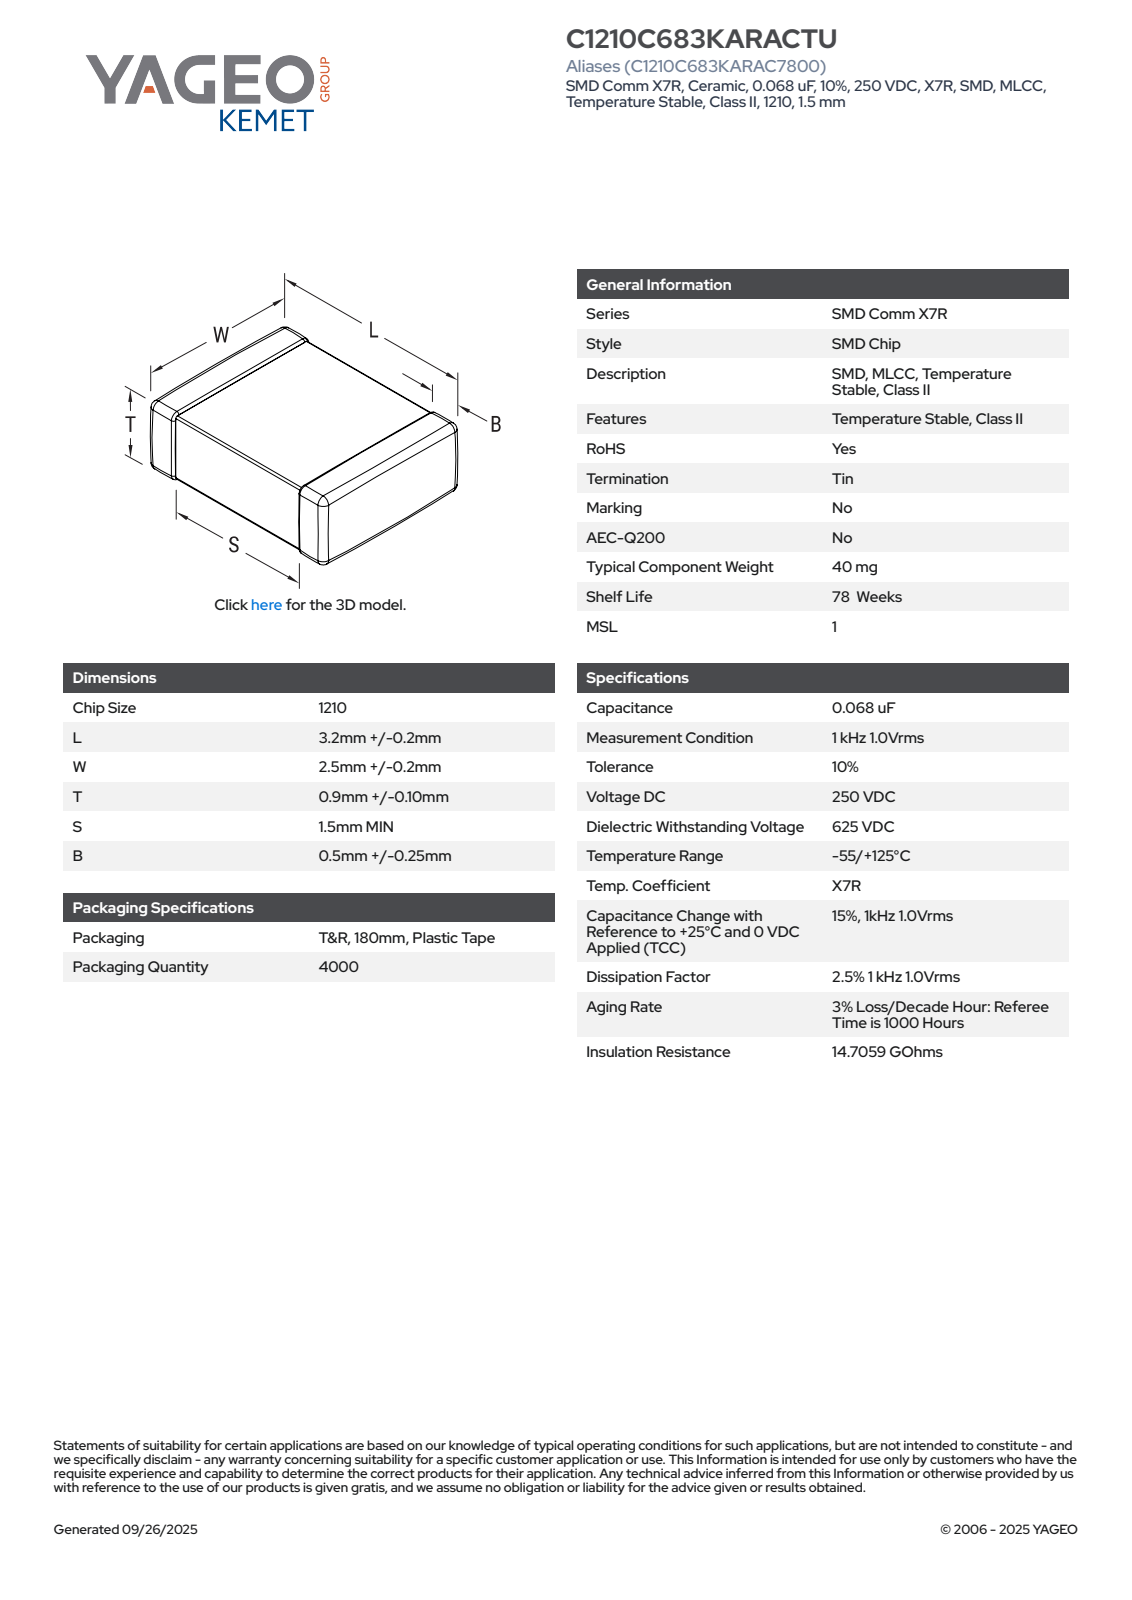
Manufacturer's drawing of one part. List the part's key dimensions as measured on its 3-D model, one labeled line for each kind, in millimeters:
Part name (STEP PRODUCT): CCS_CCSTDNOS_1210_L3.4W2.7T1B0.75
STEP written by: SolidWorks 2014 (AUTOMOTIVE_DESIGN)
Units: millimetres
Bodies: 4 solids, 125 faces (71 planar, 38 cylindrical, 16 other)
Overall size (bounding box): 3.4 × 2.7 × 1
Volume: 8 mm³ · Surface area: 30 mm²
Main face-to-face distances: 0.94, 0.88, 1, 3.4, 2.64, 2.58, 2.7, 0.95, 0.89, 1.31
